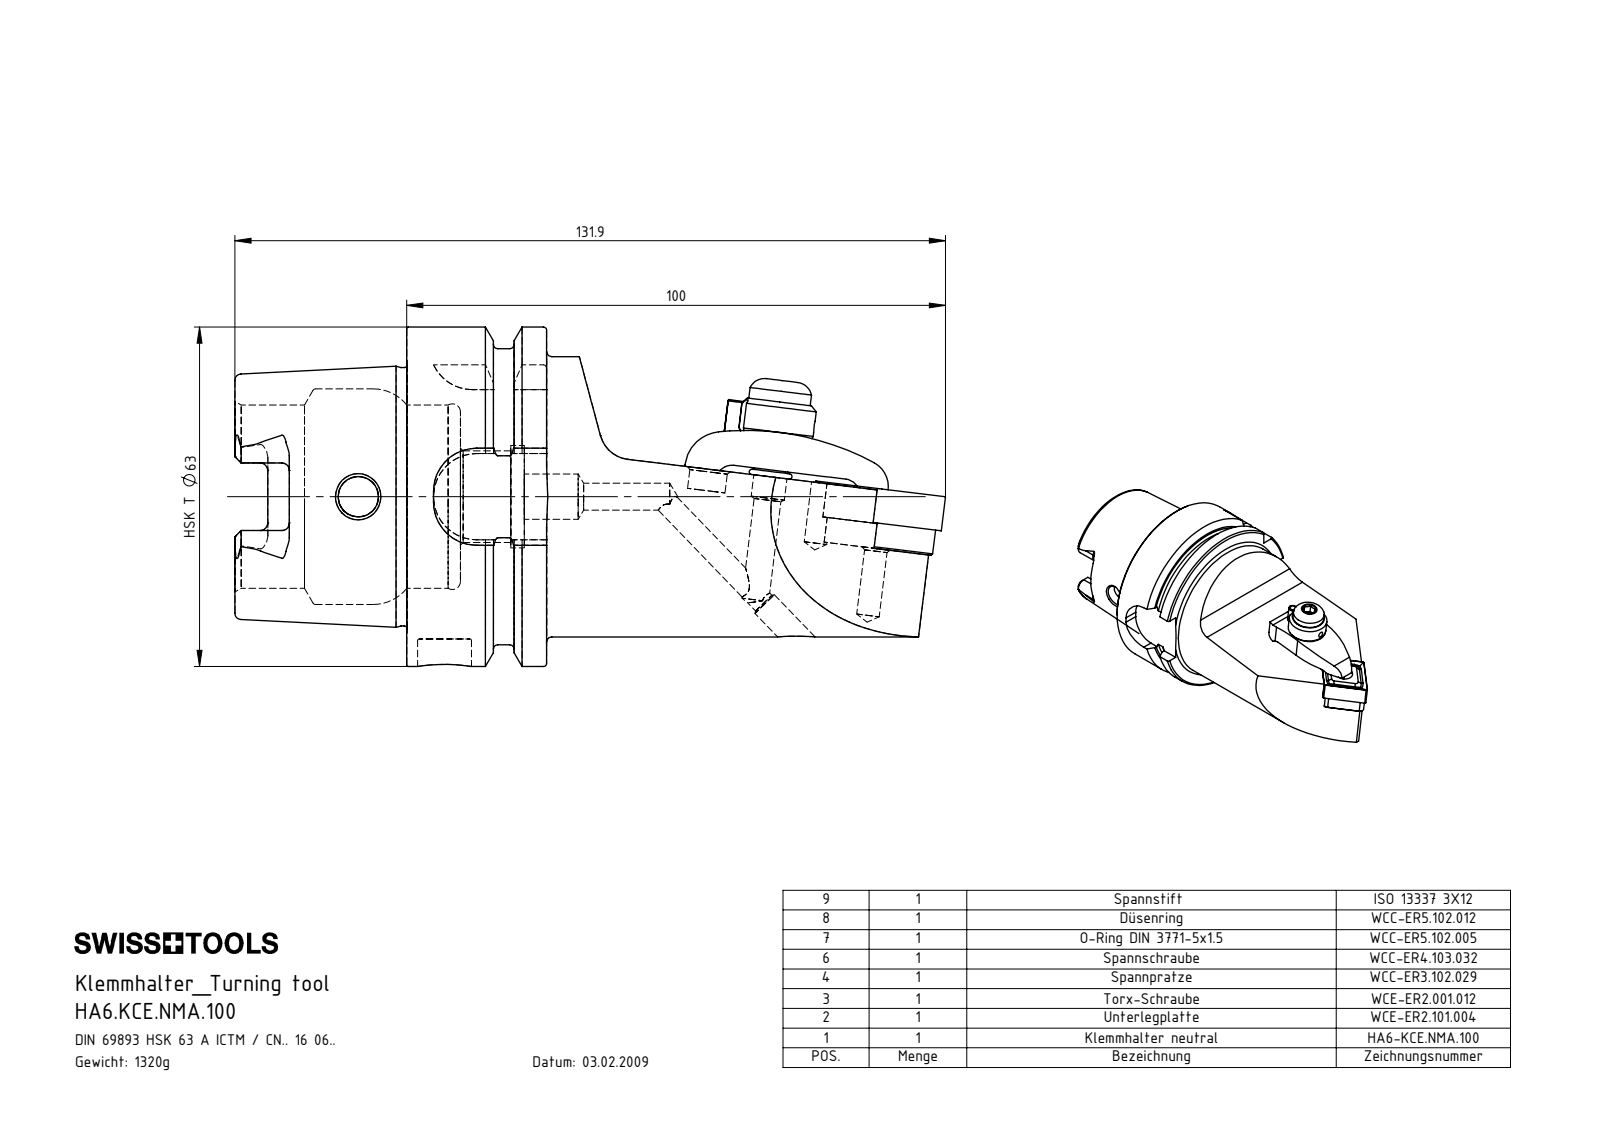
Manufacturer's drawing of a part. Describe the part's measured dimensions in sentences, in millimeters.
The part is named "WCC-ER3.102.029_C; ISO 13337 - 3 x 12_PreviewCfg; WCE-ER2.101.004_A; HA6.KCE.NMA.100 (+7 more)". Its 3-D file was written by "SolidWorks 2017 (AUTOMOTIVE_DESIGN)". It is 11 solids with 460 faces: 125 planar, 150 cylindrical and 185 other. Overall it measures 131.9 by 63 by 63 millimeters. Its volume is 167 055 cubic millimeters and its surface area 37 722 square millimeters. Round holes: 3 of diameter 2, 3 of diameter 4.2, 3 of diameter 5, 2 of diameter 7, 1 of diameter 2.4, 1 of diameter 3, 1 of diameter 4, 1 of diameter 6.2, 1 of diameter 6.35, 1 of diameter 7.5, 1 of diameter 7.9, 1 of diameter 8.4. Round bosses or shafts: 2 of diameter 5, 2 of diameter 3, 1 of diameter 63, 1 of diameter 54.95, 1 of diameter 52, 1 of diameter 47.94, 1 of diameter 14, 1 of diameter 11.5. Partial cylindrical surfaces (rounded edges, fillets, slot ends): 6 of radius 0.45, 6 of radius 1.4, 4 of radius 0.4, 4 of radius 0.79, 4 of radius 1, 4 of radius 8, 3 of radius 1.5, 2 of radius 0.79. The main face-to-face distances are 25.95, 16, 9.95, 6.06, 31.9, 41.85, 57.85, 15.06, 52.8, 21.8. The hole center spacings are 7.99, 8, 9.8, 20.6, 21.1, 28.6, 29.09, 29.1.
